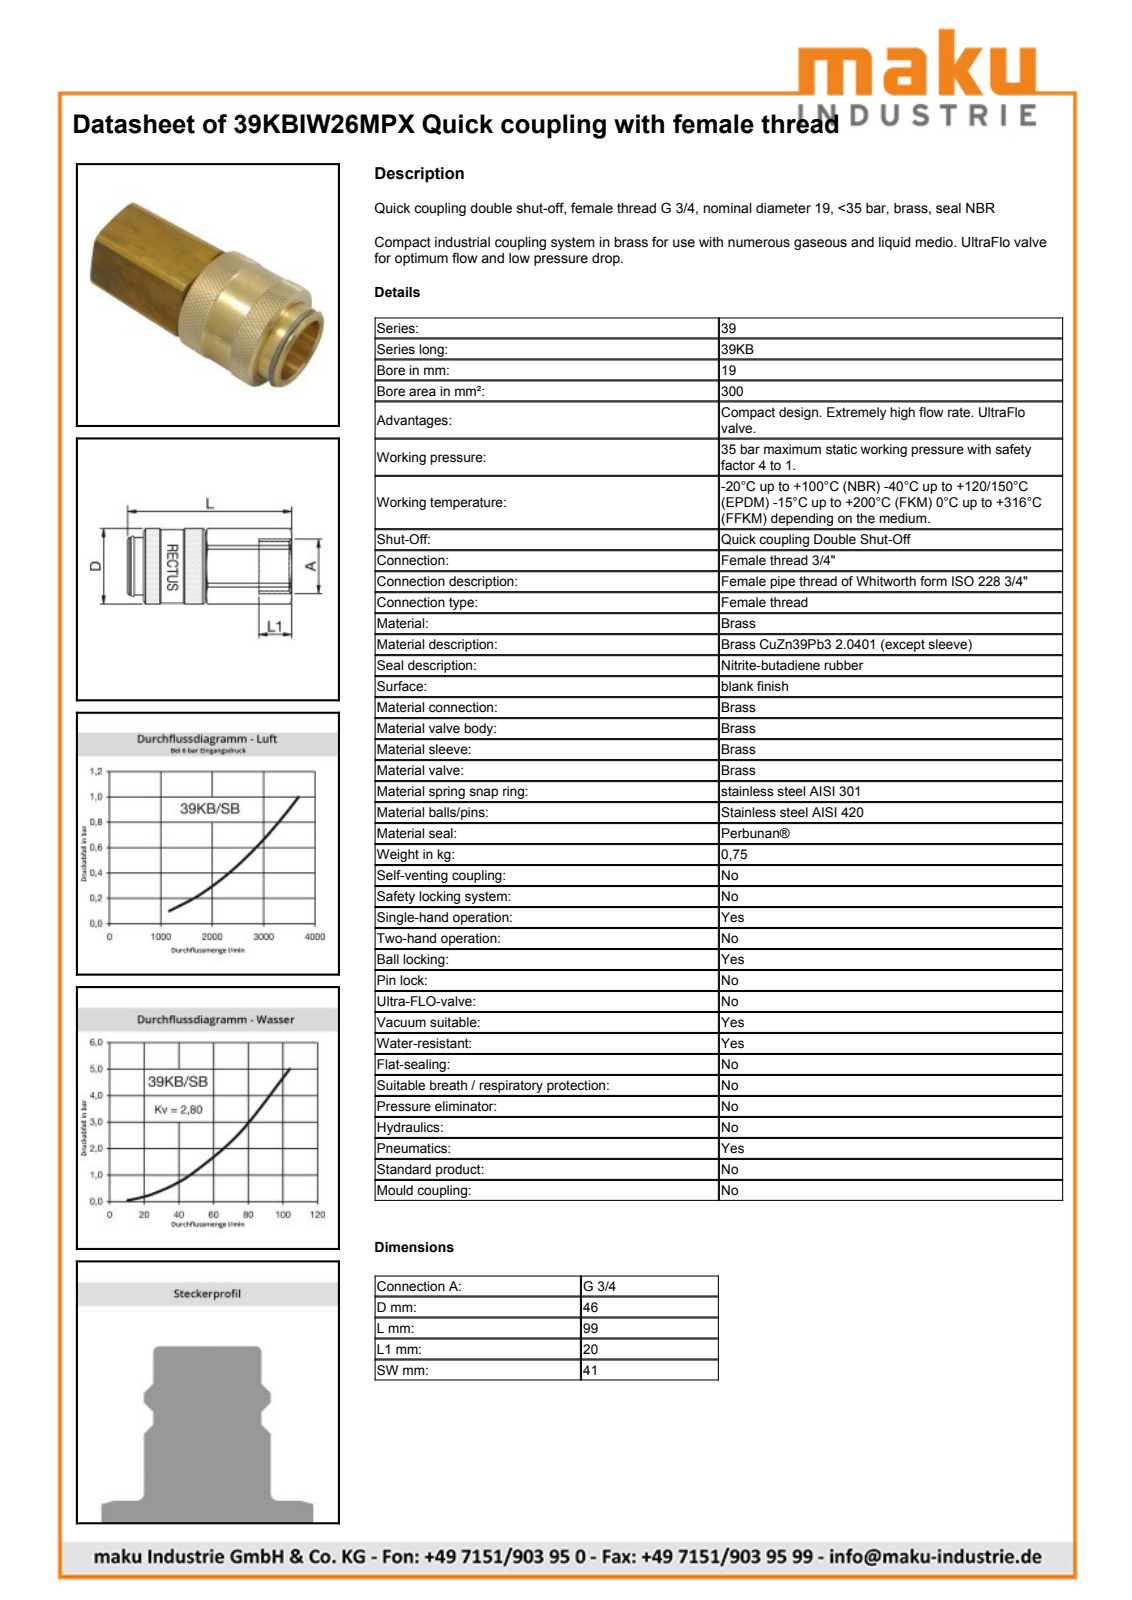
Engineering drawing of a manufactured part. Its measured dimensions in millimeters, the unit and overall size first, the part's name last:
Units: millimetres
Overall size (bounding box): 99 × 46 × 46
Round holes (diameter × count): ⌀26.44 ×1, ⌀31.5 ×1, ⌀36 ×1, ⌀39.4 ×1, ⌀41.5 ×1
Round bosses / shafts (diameter × count): ⌀46 ×1, ⌀45 ×1, ⌀38.8 ×1, ⌀35 ×1, ⌀32.6 ×1, ⌀32 ×1, ⌀29.99 ×1
Partial cylindrical surfaces — rounded edges, fillets, slot ends (radius × count): R22.4 ×1, R22.98 ×1
Main face-to-face distances: 41, 99, 27.25, 71.75, 89.5, 62.25, 9.5, 47, 52, 24.75
Volume: 121 121 mm³ · Surface area: 34 919 mm²
Bodies: 2 solids, 507 faces (183 planar, 68 cylindrical, 256 other)
Part name (STEP PRODUCT): D104961
STEP written by: Autodesk Inventor 2013 (AUTOMOTIVE_DESIGN)
